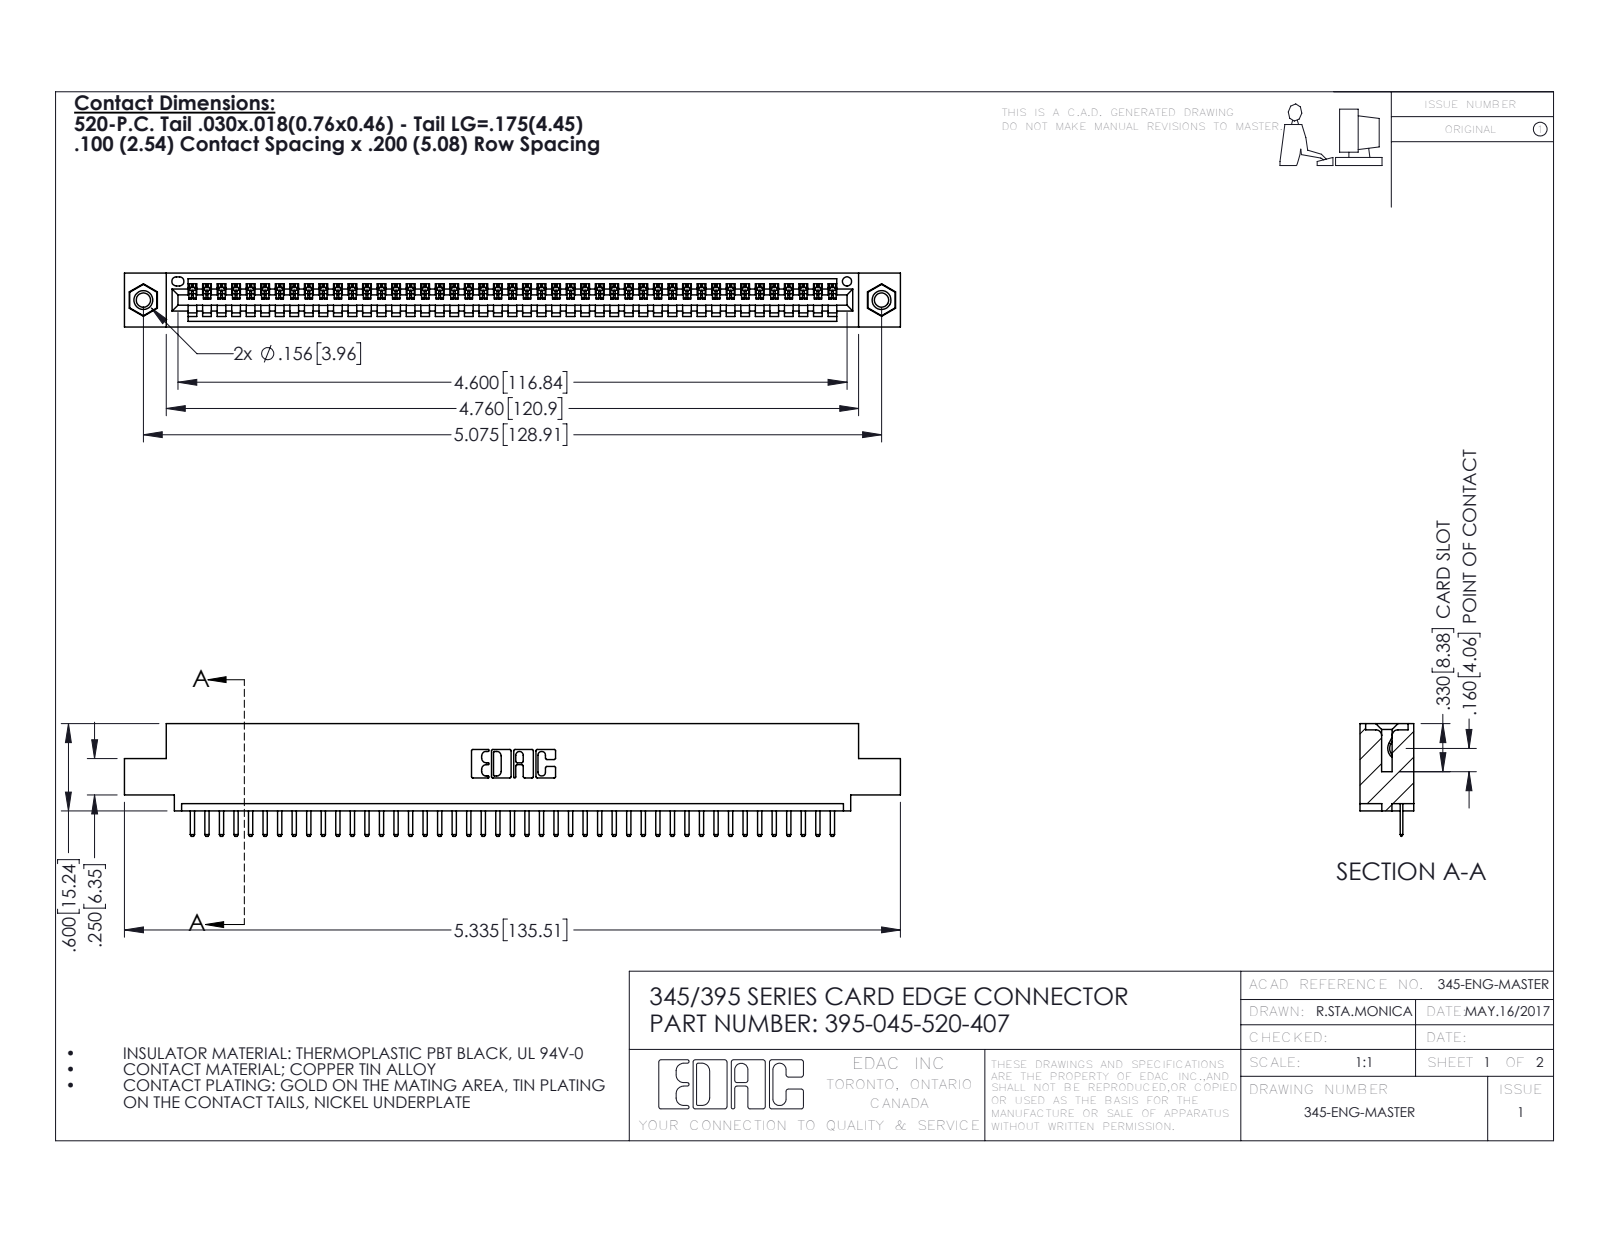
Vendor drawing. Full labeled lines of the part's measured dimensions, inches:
Part name (STEP PRODUCT): 345-292-001_345-293-120; 345-250-001_345-250-005-103; 345 Part_0.110 Offset - 0.156 Dia-TI; 395-045-520-407
STEP written by: SolidWorks 2016 (CONFIG_CONTROL_DESIGN)
Units: inches
Bodies: 48 solids, 2980 faces (2006 planar, 958 cylindrical, 16 other)
Overall size (bounding box): 5.335 × 0.775 × 0.37
Volume: 0.774 in³ · Surface area: 25.7 in²
Round holes (diameter × count): ⌀0.098 ×2, ⌀0.125 ×2, ⌀0.156 ×2, ⌀0.064 ×1
Round bosses / shafts (diameter × count): ⌀0.155 ×2
Partial cylindrical surfaces — rounded edges, fillets, slot ends (radius × count): R0.01 ×92, R0.006 ×90, R0.01 ×22, R0.007 ×6, R0.031 ×6, R0.026 ×3, R0.031 ×2, R0.04 ×2
Main face-to-face distances: 0.072, 0.298, 0.37, 0.2, 0.098, 0.272, 0.025, 0.225, 0.072, 0.149
Hole centre spacings: 0.27, 4.839, 5.075
